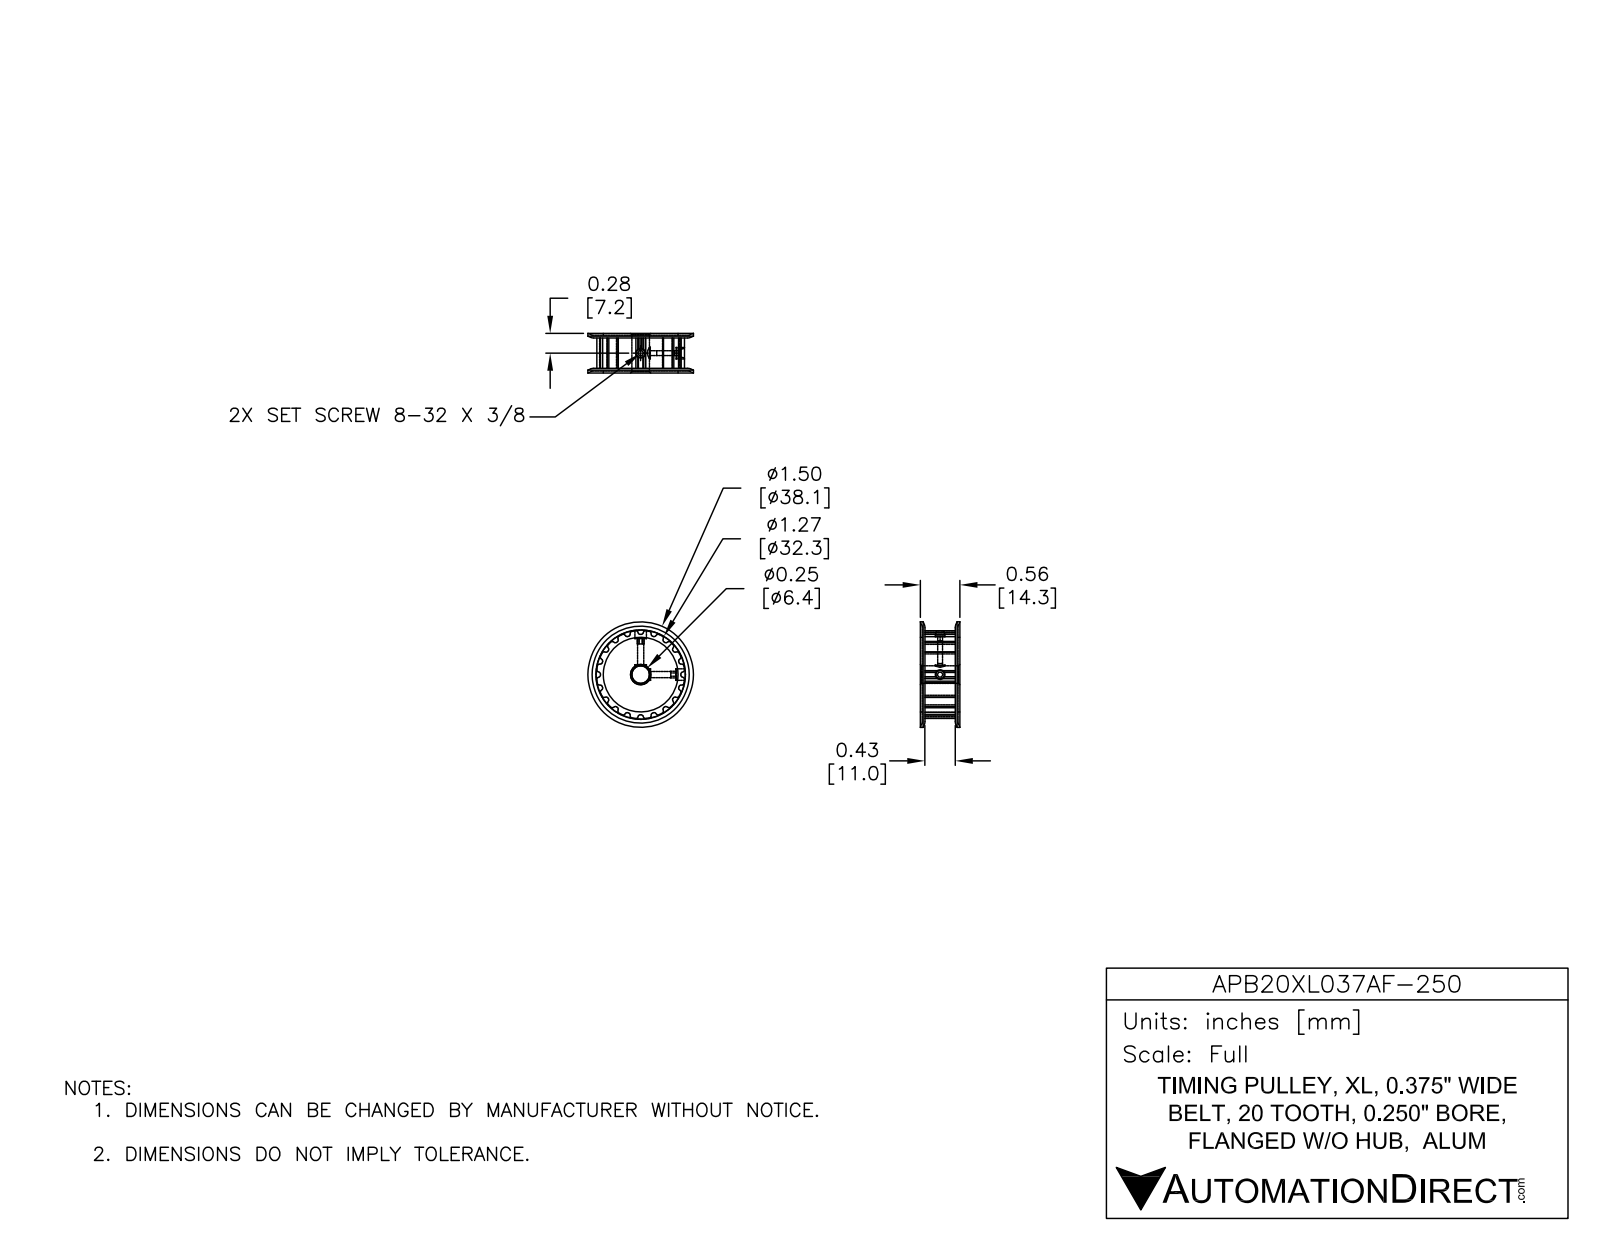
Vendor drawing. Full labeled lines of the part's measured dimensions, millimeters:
Part name (STEP PRODUCT): APB20XL037AF-250
STEP written by: SolidWorks 2014 (AUTOMOTIVE_DESIGN)
Units: millimetres
Bodies: 1 solid, 233 faces (72 planar, 137 cylindrical, 24 other)
Overall size (bounding box): 38.1 × 38.1 × 14.3
Volume: 9 700 mm³ · Surface area: 5 135 mm²
Round holes (diameter × count): ⌀2.2 ×2, ⌀3.2 ×2, ⌀6.4 ×1
Round bosses / shafts (diameter × count): ⌀12.6 ×1
Partial cylindrical surfaces — rounded edges, fillets, slot ends (radius × count): R0.4 ×80, R14.5 ×1
Main face-to-face distances: 12.7, 0.8, 11.1, 31.8, 13.5, 1.6, 11.9, 14.3, 11.1
